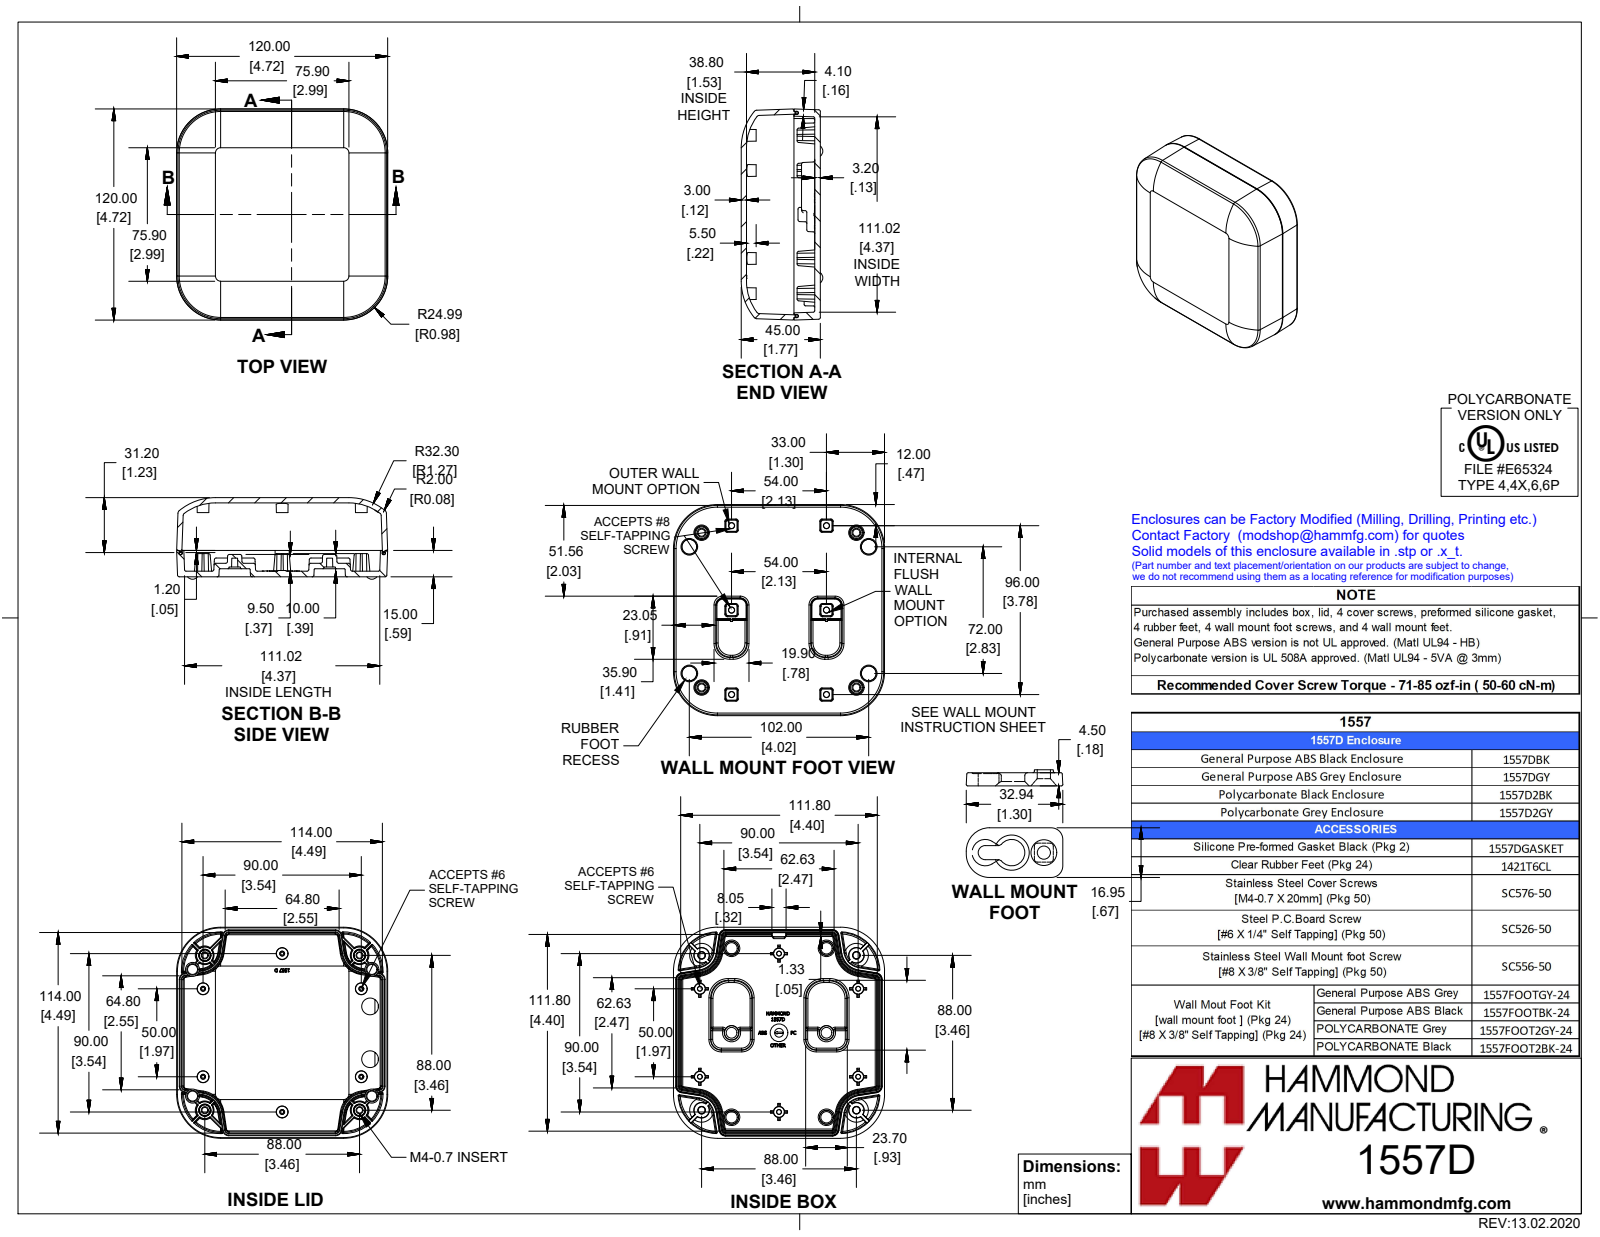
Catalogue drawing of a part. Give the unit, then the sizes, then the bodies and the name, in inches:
Units: inches
Overall size (bounding box): 5.864 × 4.724 × 1.949
Round holes (diameter × count): ⌀0.128 ×4, ⌀0.177 ×4
Round bosses / shafts (diameter × count): ⌀0.071 ×12, ⌀0.313 ×4, ⌀0.303 ×4, ⌀0.25 ×4, ⌀0.218 ×4, ⌀0.21 ×4, ⌀0.165 ×4, ⌀0.153 ×4
Partial cylindrical surfaces — rounded edges, fillets, slot ends (radius × count): R0.02 ×101, R0.039 ×79, R0.157 ×12, R0.008 ×8, R0.012 ×8, R0.016 ×8, R0.059 ×8, R0.083 ×8
Main face-to-face distances: 0.126, 0.118, 1.772, 1.654, 1.528, 1.646, 0.118, 4.602, 4.72, 0.161
Hole centre spacings: 0.687, 2.8, 3.465, 3.683, 4.575, 2.126, 3.78, 4.337
Volume: 10.58 in³ · Surface area: 194.5 in²
Bodies: 23 solids, 2803 faces (925 planar, 571 cylindrical, 1307 other)
Part name (STEP PRODUCT): 1557DBK; Wall Mount Foot; 1557H Gaskets; PFR1421T4 (+5 more)
STEP written by: SolidWorks 2019 (CONFIG_CONTROL_DESIGN)
